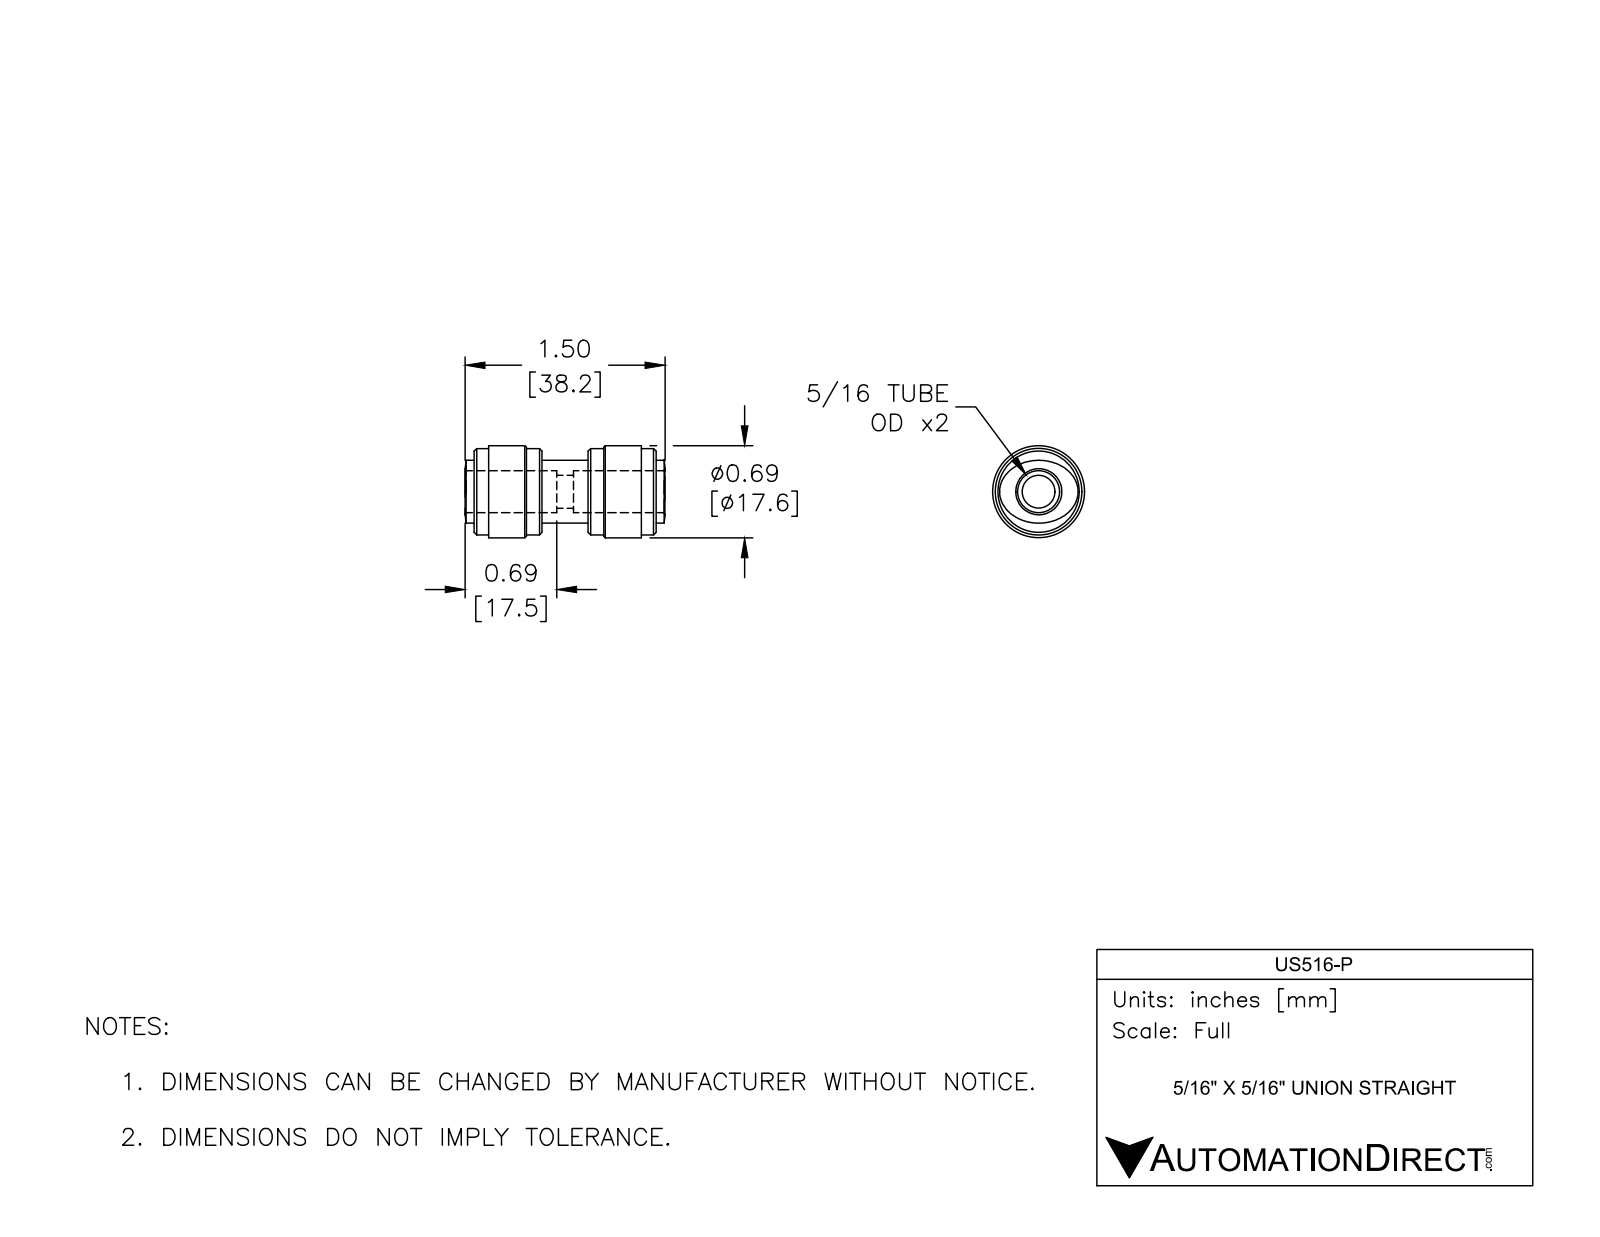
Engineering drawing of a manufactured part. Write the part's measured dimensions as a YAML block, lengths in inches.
part_name: "US516-P"
step_written_by: "SolidWorks 2017 (AUTOMOTIVE_DESIGN)"
units: inches
bodies: {solids: 1, faces: 54, planar: 10, cylindrical: 20, other: 24}
overall_size: [1.504, 0.693, 0.693]
volume: 0.339
surface_area: 5.266
round_holes:
  - {diameter: 0.248, count: 1}
  - {diameter: 0.315, count: 1}
round_bosses_or_shafts:
  - {diameter: 0.693, count: 1}
  - {diameter: 0.65, count: 1}
  - {diameter: 0.472, count: 1}
face_to_face_distances: [0.512, 0.11, 0.748, 0.858, 0.346, 1.26, 0.402, 1.37, 0.622, 0.638]
